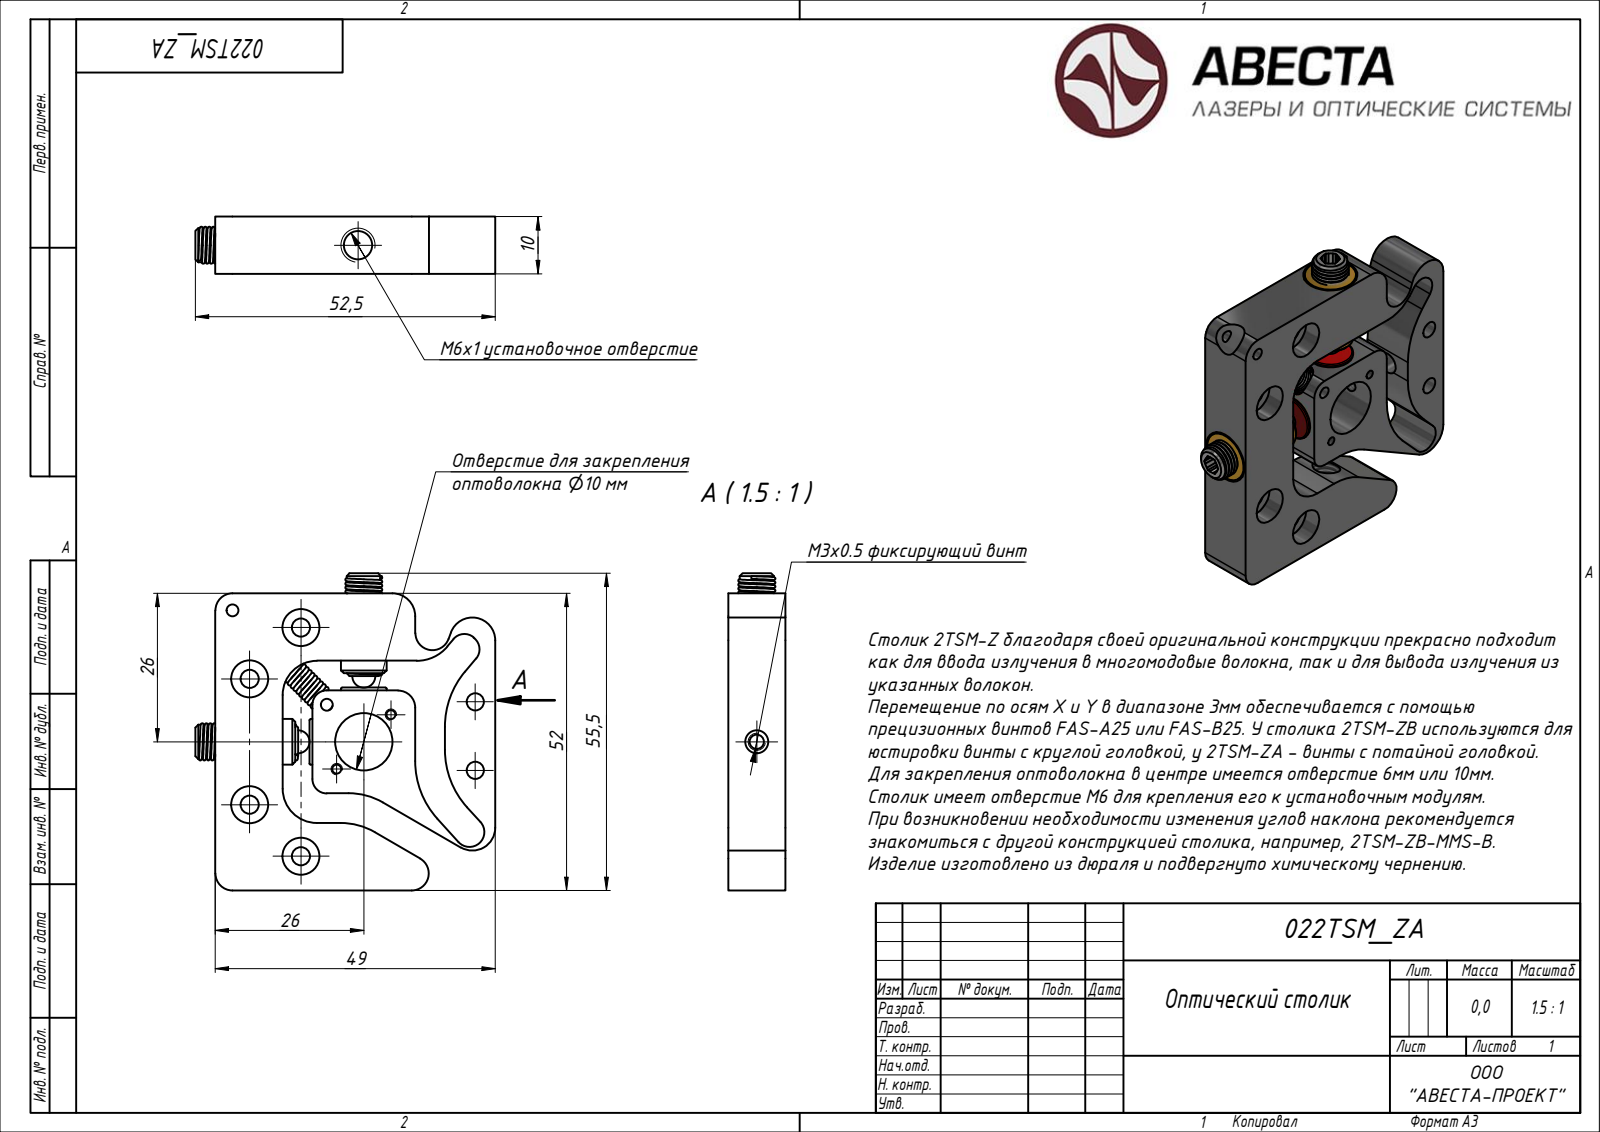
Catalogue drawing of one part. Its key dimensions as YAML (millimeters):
part_name: "Block 01; Block 02"
step_written_by: "ST-DEVELOPER v15 (AUTOMOTIVE_DESIGN)"
units: millimeters
bodies: {solids: 9, faces: 281, planar: 0, cylindrical: 0, other: 281}
overall_size: [55.5, 52.5, 10]
